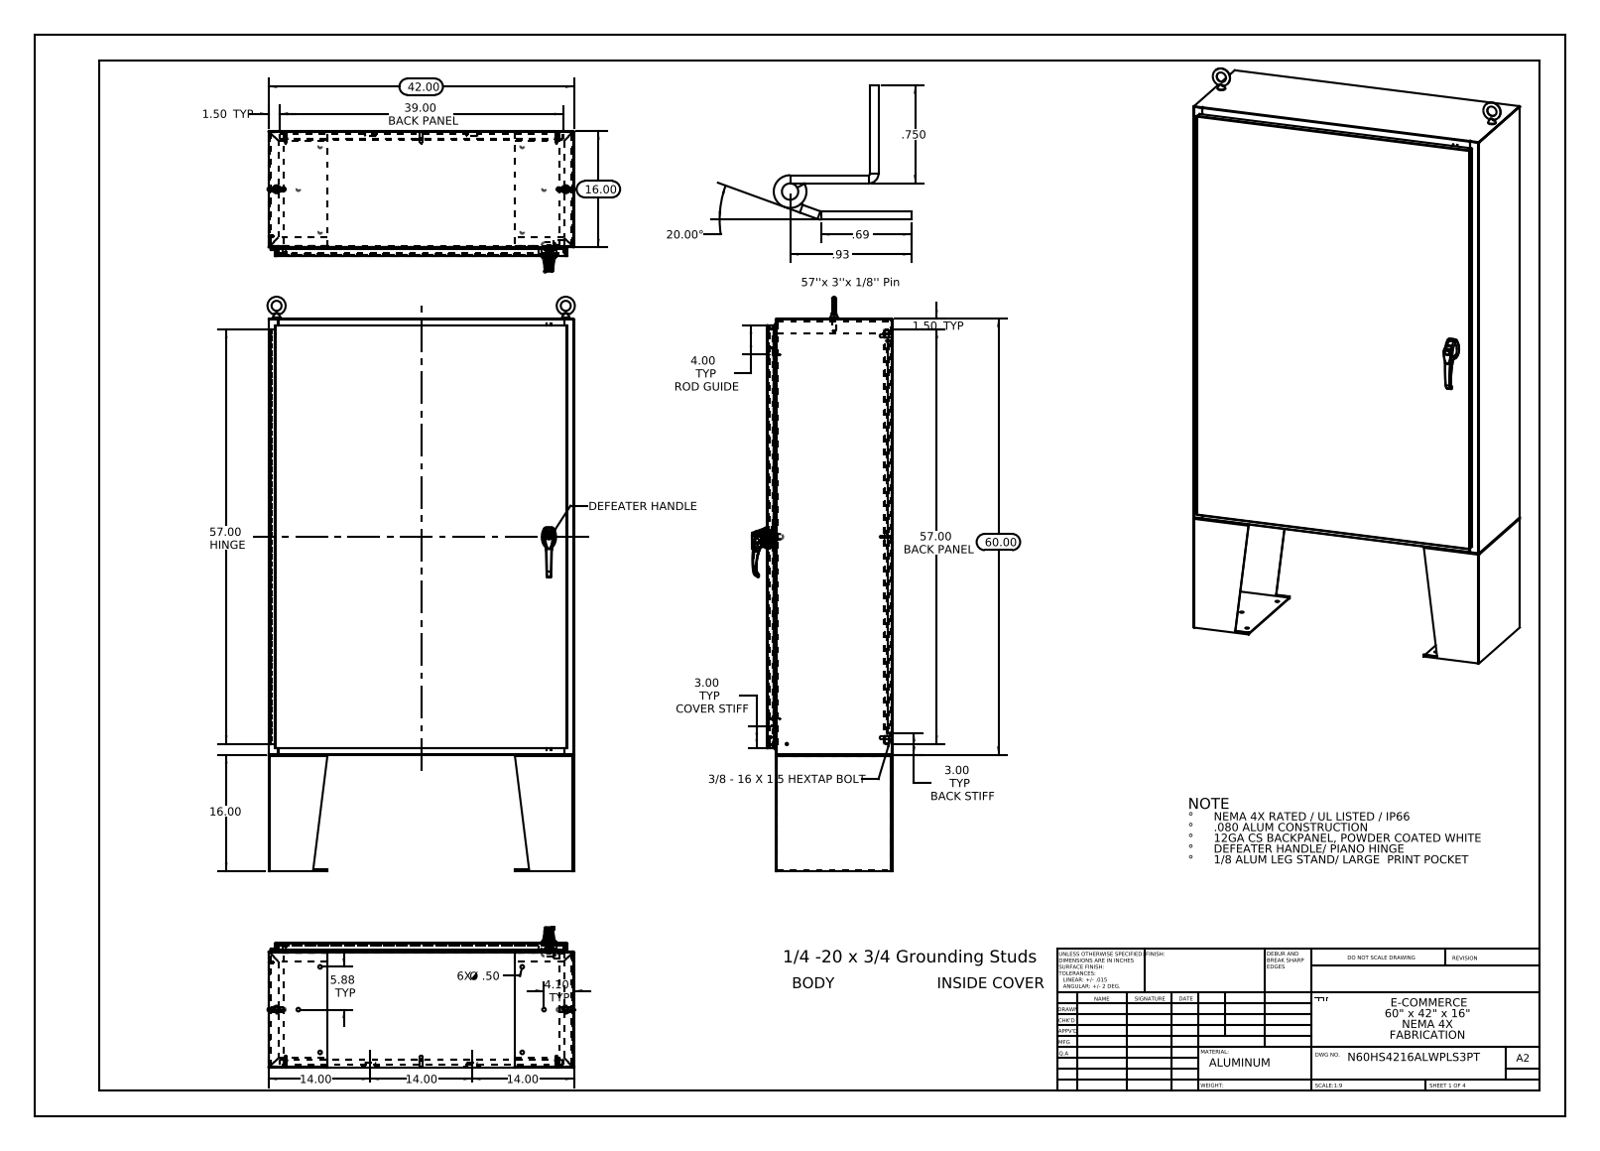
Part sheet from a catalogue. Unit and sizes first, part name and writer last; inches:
Units: inches
Overall size (bounding box): 79 × 42.271 × 19.307
Round holes (diameter × count): ⌀0.5 ×14, ⌀0.25 ×10, ⌀0.75 ×4, ⌀0.138 ×3, ⌀0.161 ×3, ⌀0.079 ×2, ⌀0.203 ×2, ⌀0.313 ×2, ⌀0.437 ×2, ⌀0.125 ×1, ⌀0.125 ×1, ⌀0.197 ×1
Round bosses / shafts (diameter × count): ⌀0.625 ×10, ⌀0.157 ×10, ⌀0.14 ×10, ⌀0.375 ×8, ⌀0.33 ×8, ⌀0.315 ×3, ⌀0.236 ×3, ⌀1.181 ×1
Partial cylindrical surfaces — rounded edges, fillets, slot ends (radius × count): R0.118 ×37, R0.013 ×34, R0.006 ×33, R0.088 ×28, R0.039 ×15, R0.028 ×12, R0.039 ×8, R0.143 ×8
Main face-to-face distances: 0.075, 17.126, 0.104, 17.051, 1.075, 17.201, 1, 16.126, 16.051, 1.179
Hole centre spacings: 8.393, 16.578, 23.354, 25.662, 27.625, 31.348, 33.317, 34.289
Volume: 1 115 in³ · Surface area: 26 823 in²
Bodies: 55 solids, 3808 faces (1529 planar, 1461 cylindrical, 818 other)
Part name (STEP PRODUCT): 022151; 297025; 21130102; N60HS4216SSWPLS3PT Enclosure Stiffener (+8 more)
STEP written by: SolidWorks 2013 (CONFIG_CONTROL_DESIGN)
